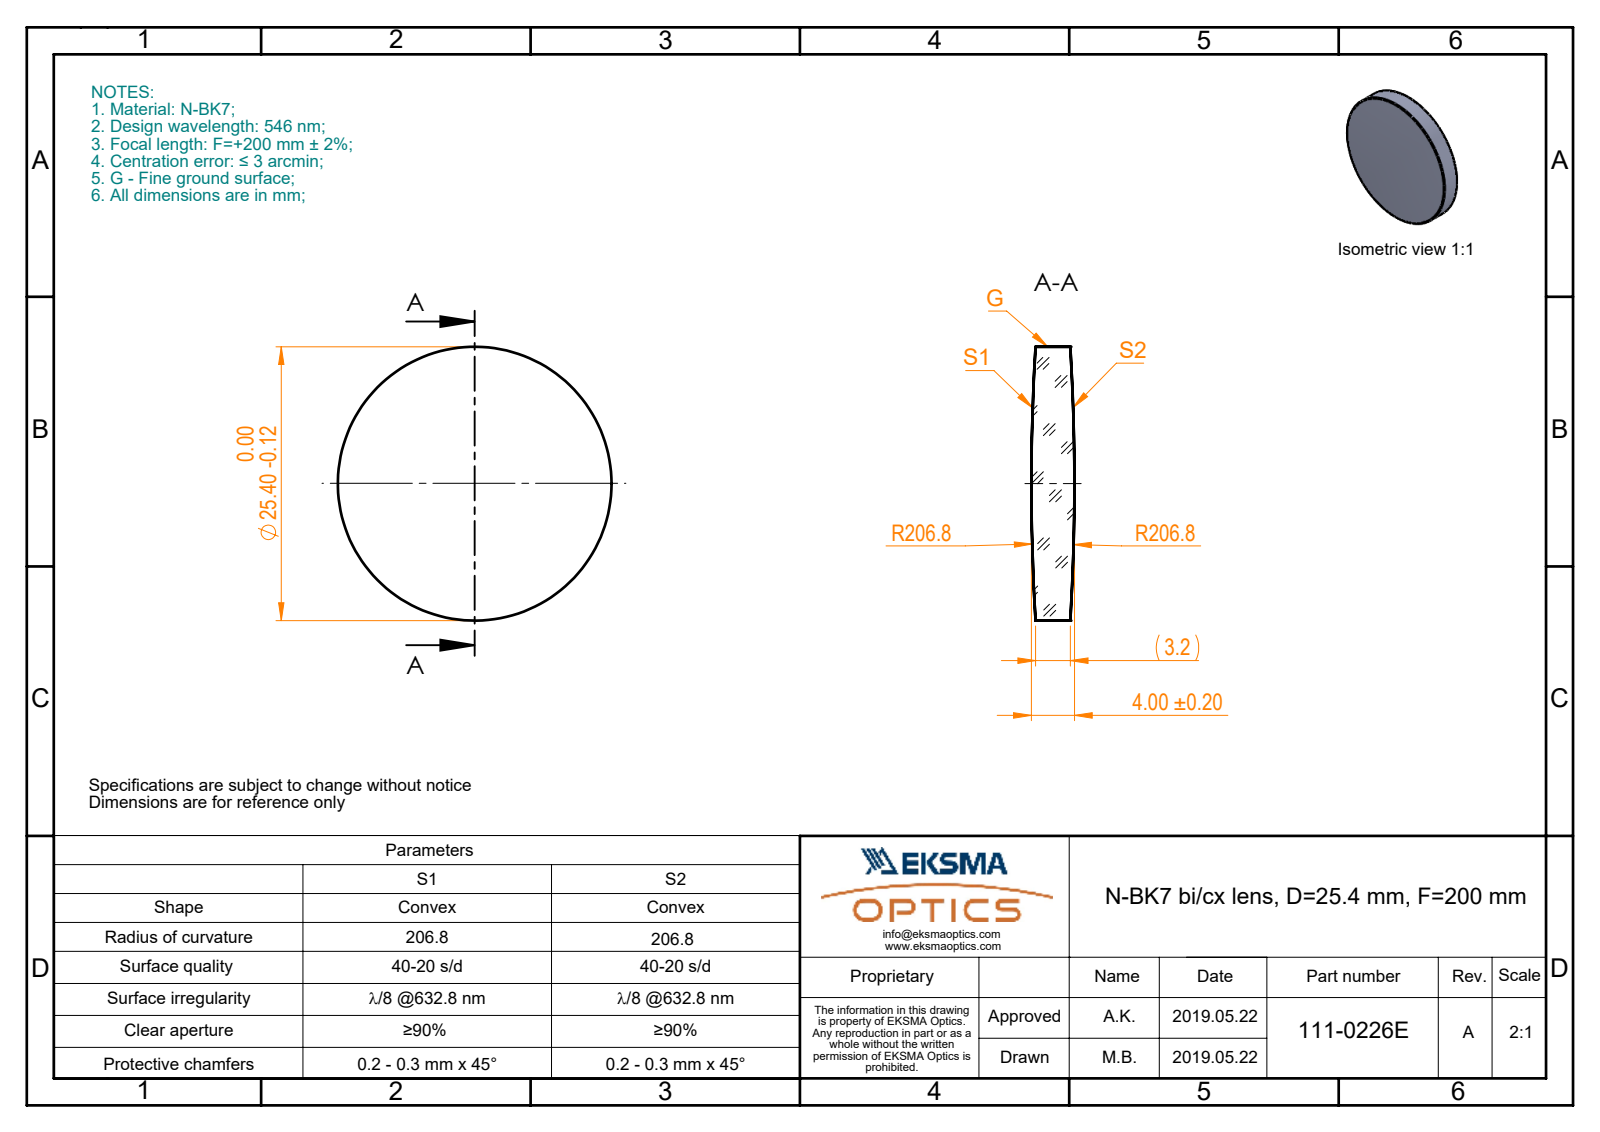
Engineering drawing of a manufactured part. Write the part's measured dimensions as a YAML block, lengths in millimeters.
part_name: "111-0226E BK7 bi-cx 25.4 F200"
step_written_by: "SolidWorks 2017 (CONFIG_CONTROL_DESIGN)"
units: millimeters
bodies: {solids: 1, faces: 6, planar: 0, cylindrical: 2, other: 4}
overall_size: [25.4, 25.4, 4]
volume: 1829
surface_area: 1271
round_bosses_or_shafts:
  - {diameter: 25.4, count: 1}
